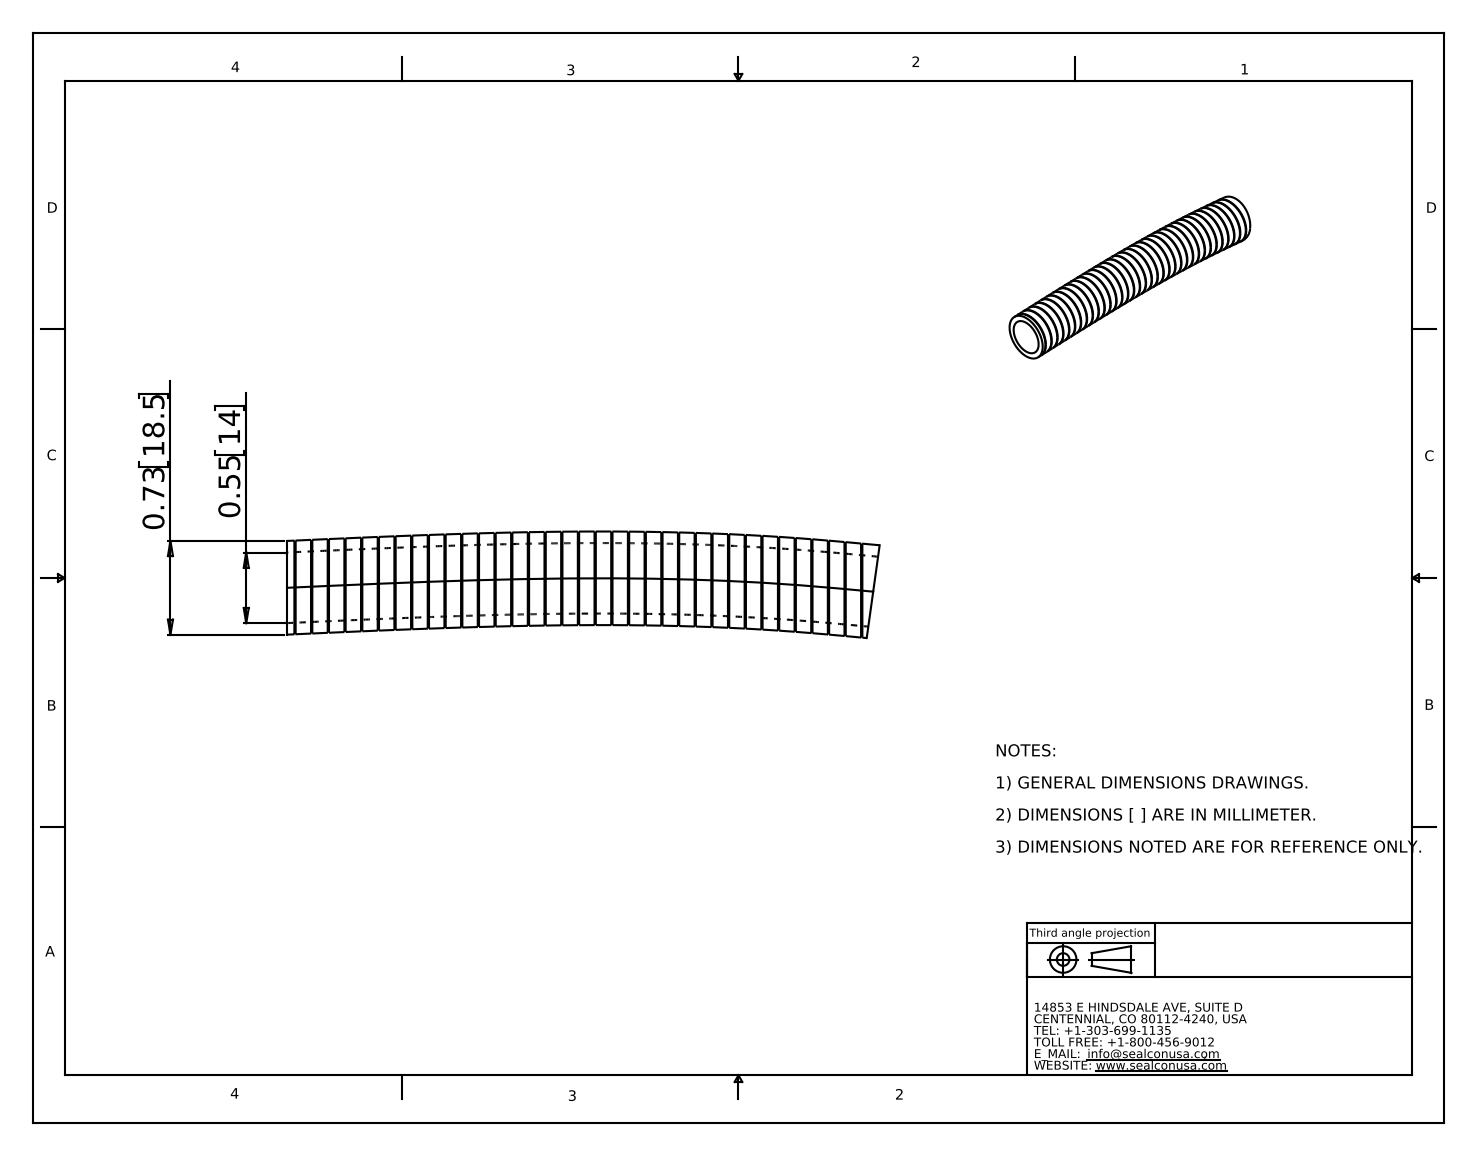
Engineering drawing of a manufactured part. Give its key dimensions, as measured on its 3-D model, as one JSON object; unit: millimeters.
{"part_name": "SM-1013-HY", "step_written_by": "SolidWorks 2007 (AUTOMOTIVE_DESIGN)", "units": "millimeters", "bodies": {"solids": 1, "faces": 216, "planar": 72, "cylindrical": 70, "other": 74}, "overall_size": [117.3, 21.1, 18.5], "volume_mm3": 12600, "surface_area_mm2": 19200, "round_bosses_or_shafts": [[14.6, 34]], "face_to_face_distances": [3.3, 6.6, 3.3, 3.6, 6.8, 9.9, 3, 9.9, 13.2, 6.6]}
